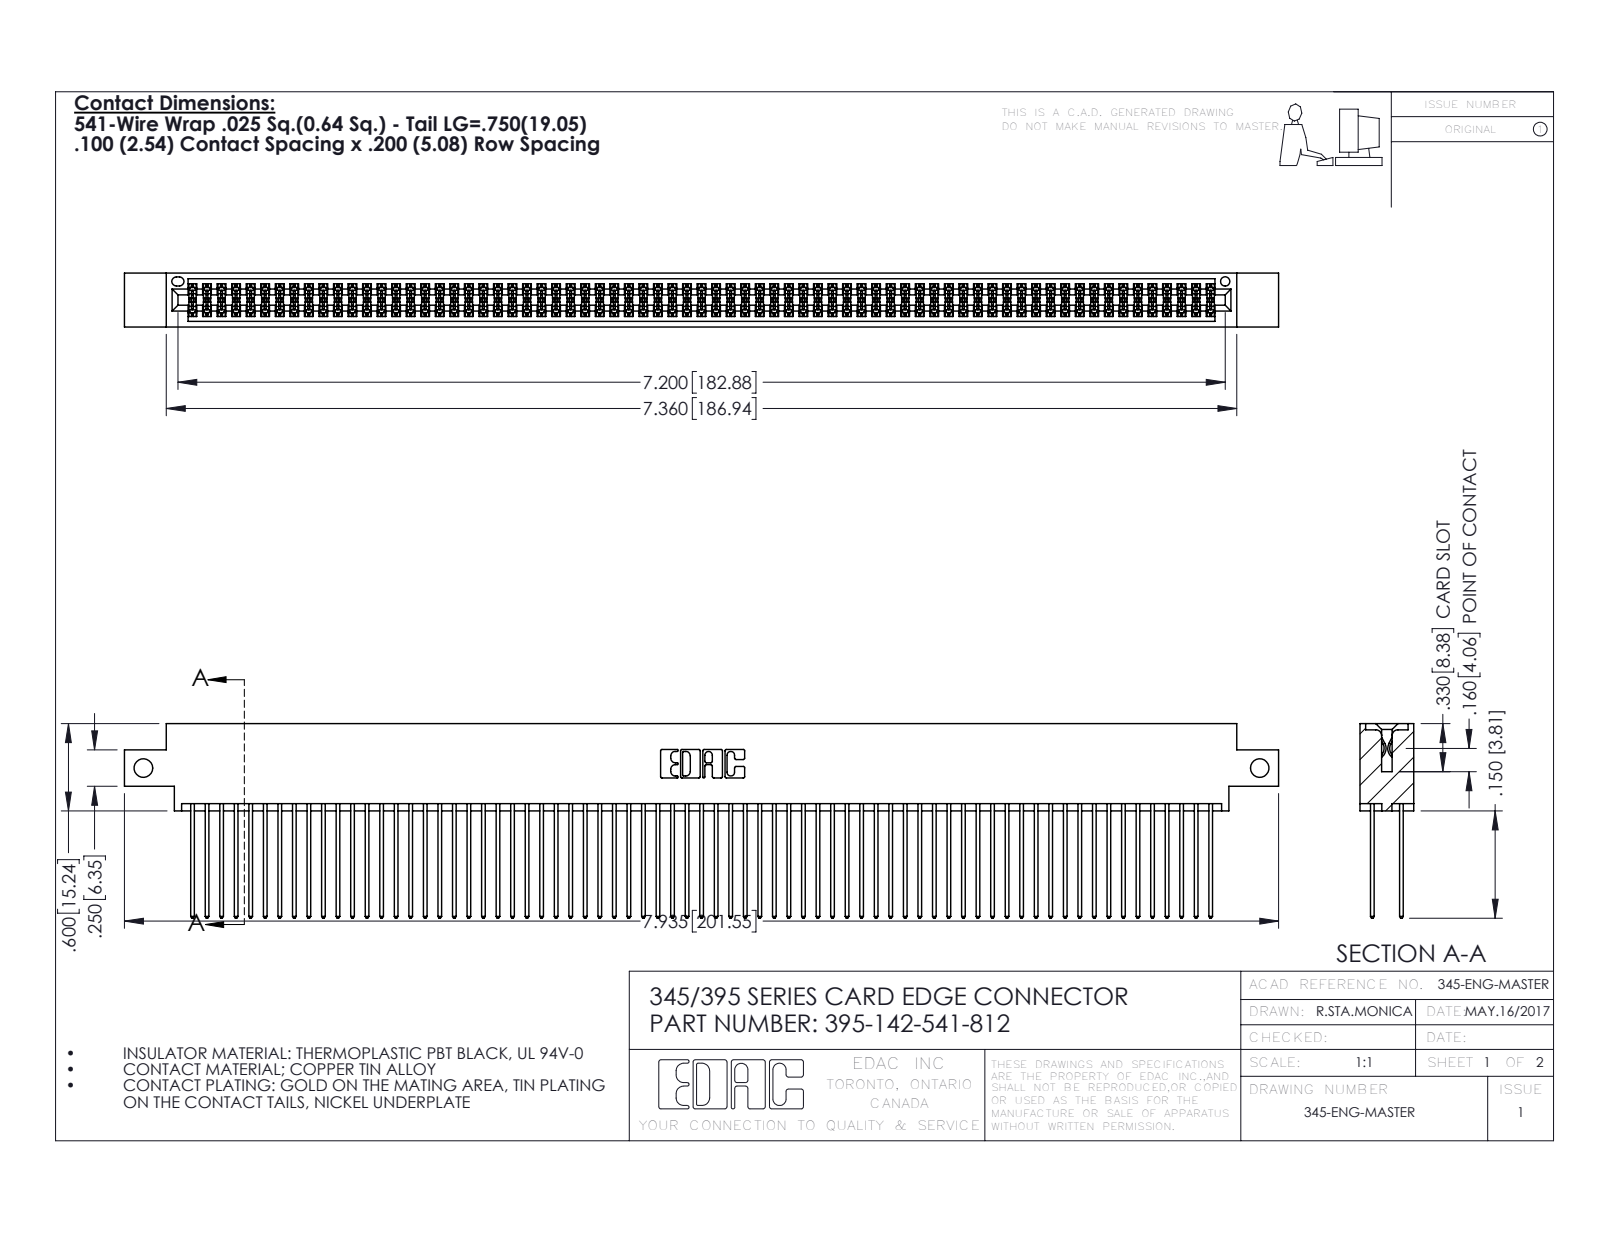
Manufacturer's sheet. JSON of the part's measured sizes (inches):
{"part_name": "345-292-001_345-293-141; 395-142-541-812; 345 Part_0.170 Offset - Side Mount", "step_written_by": "SolidWorks 2016 (CONFIG_CONTROL_DESIGN)", "units": "inches", "bodies": {"solids": 143, "faces": 7230, "planar": 4770, "cylindrical": 2460, "other": 0}, "overall_size": [7.935, 1.337, 0.37], "volume_in3": 1.249, "surface_area_in2": 53.7, "round_holes": [[0.128, 2], [0.064, 1]], "partial_cylinders_radius": [[0.006, 213], [0.01, 142], [0.01, 22], [0.007, 6], [0.031, 6], [0.026, 3], [0.014, 2], [0.019, 2]], "face_to_face_distances": [0.298, 0.072, 0.2, 0.098, 0.272, 0.025, 0.225, 0.37, 0.175, 0.149], "hole_center_spacings": [7.675]}
